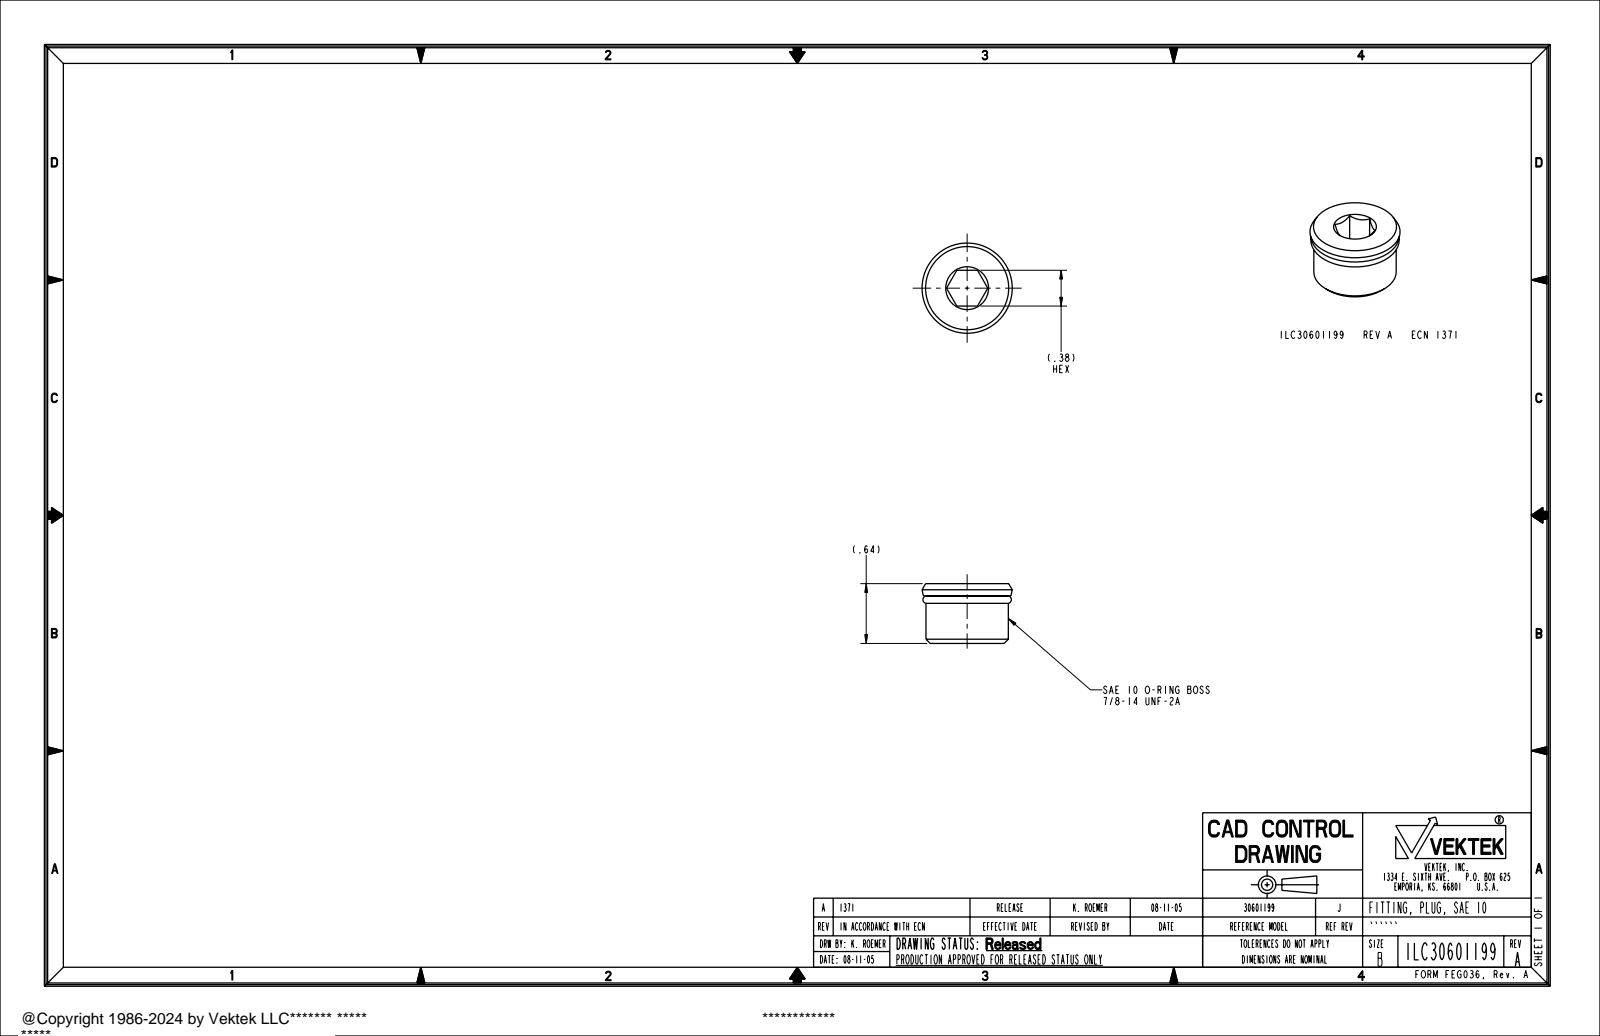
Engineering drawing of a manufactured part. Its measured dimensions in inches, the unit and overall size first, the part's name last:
Units: inches
Overall size (bounding box): 0.958 × 0.958 × 0.635
Round bosses / shafts (diameter × count): ⌀0.875 ×1
Main face-to-face distances: 0.635, 0.38, 0.305, 0.33, 0.505, 0.2, 0.13
Volume: 0.353 in³ · Surface area: 3.536 in²
Bodies: 1 solid, 24 faces (10 planar, 4 cylindrical, 10 other)
Part name (STEP PRODUCT): ILC30601199
STEP written by: PRO/ENGINEER BY PARAMETRIC TECHNOLOGY CORPORATION, 2004290 (AUTOMOTIVE_DESIGN_CC2)
